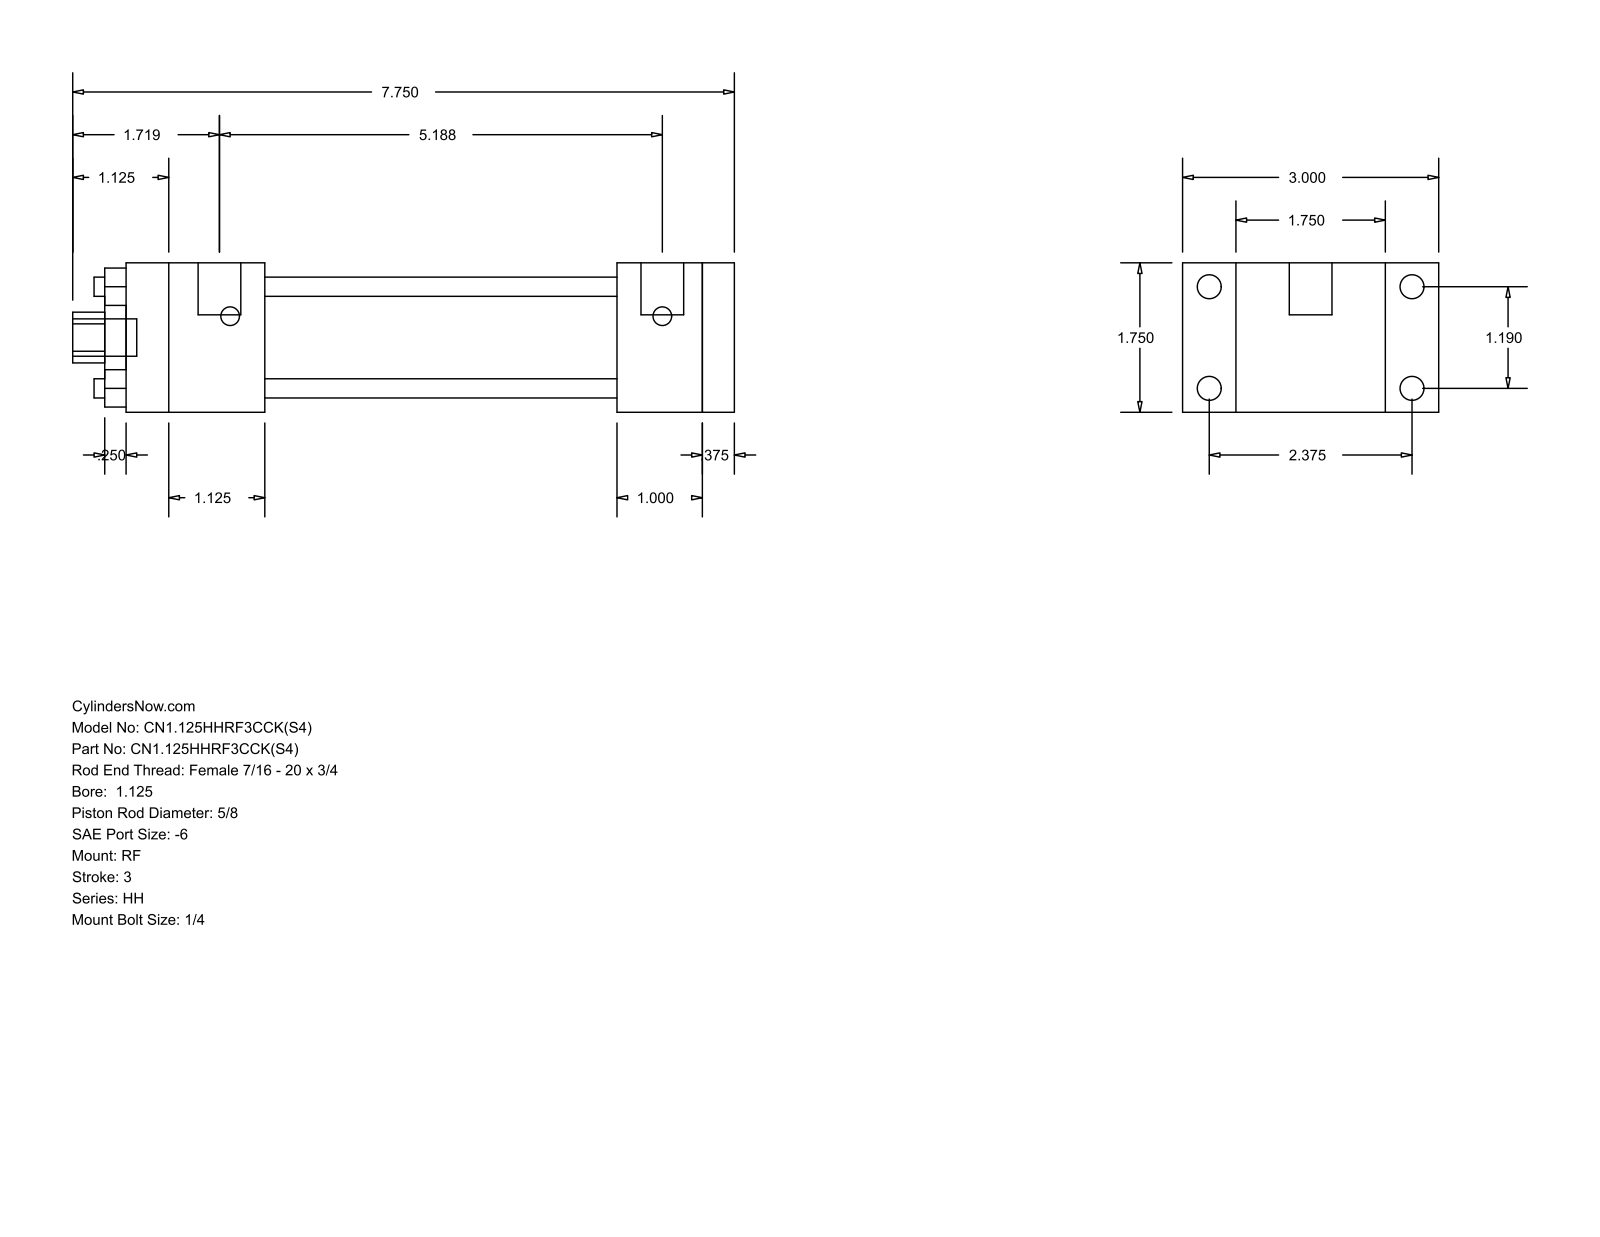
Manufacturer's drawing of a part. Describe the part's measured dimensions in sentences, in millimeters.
The part is named "HH_RF__0112_0.625". Its 3-D file was written by "GSSL Pune (CONFIG_CONTROL_DESIGN)". It is 0 solids with 92 faces: 64 planar, 28 cylindrical and 0 other. Overall it measures 196.85 by 76.2 by 44.45 millimeters. Round holes: 4 of diameter 5.71, 1 of diameter 15.88, 1 of diameter 28.57, 1 of diameter 34.92. Round bosses or shafts: 4 of diameter 7.14, 4 of diameter 5.56, 2 of diameter 12.7, 1 of diameter 11.11. Partial cylindrical surfaces (rounded edges, fillets, slot ends): 1 of radius 7.54. The main face-to-face distances are 44.46, 9.53, 180.97, 15.87, 130.17, 139.7, 104.78, 25.39, 34.92, 41.27. The hole center spacings are 21.37, 30.22, 42.74.
